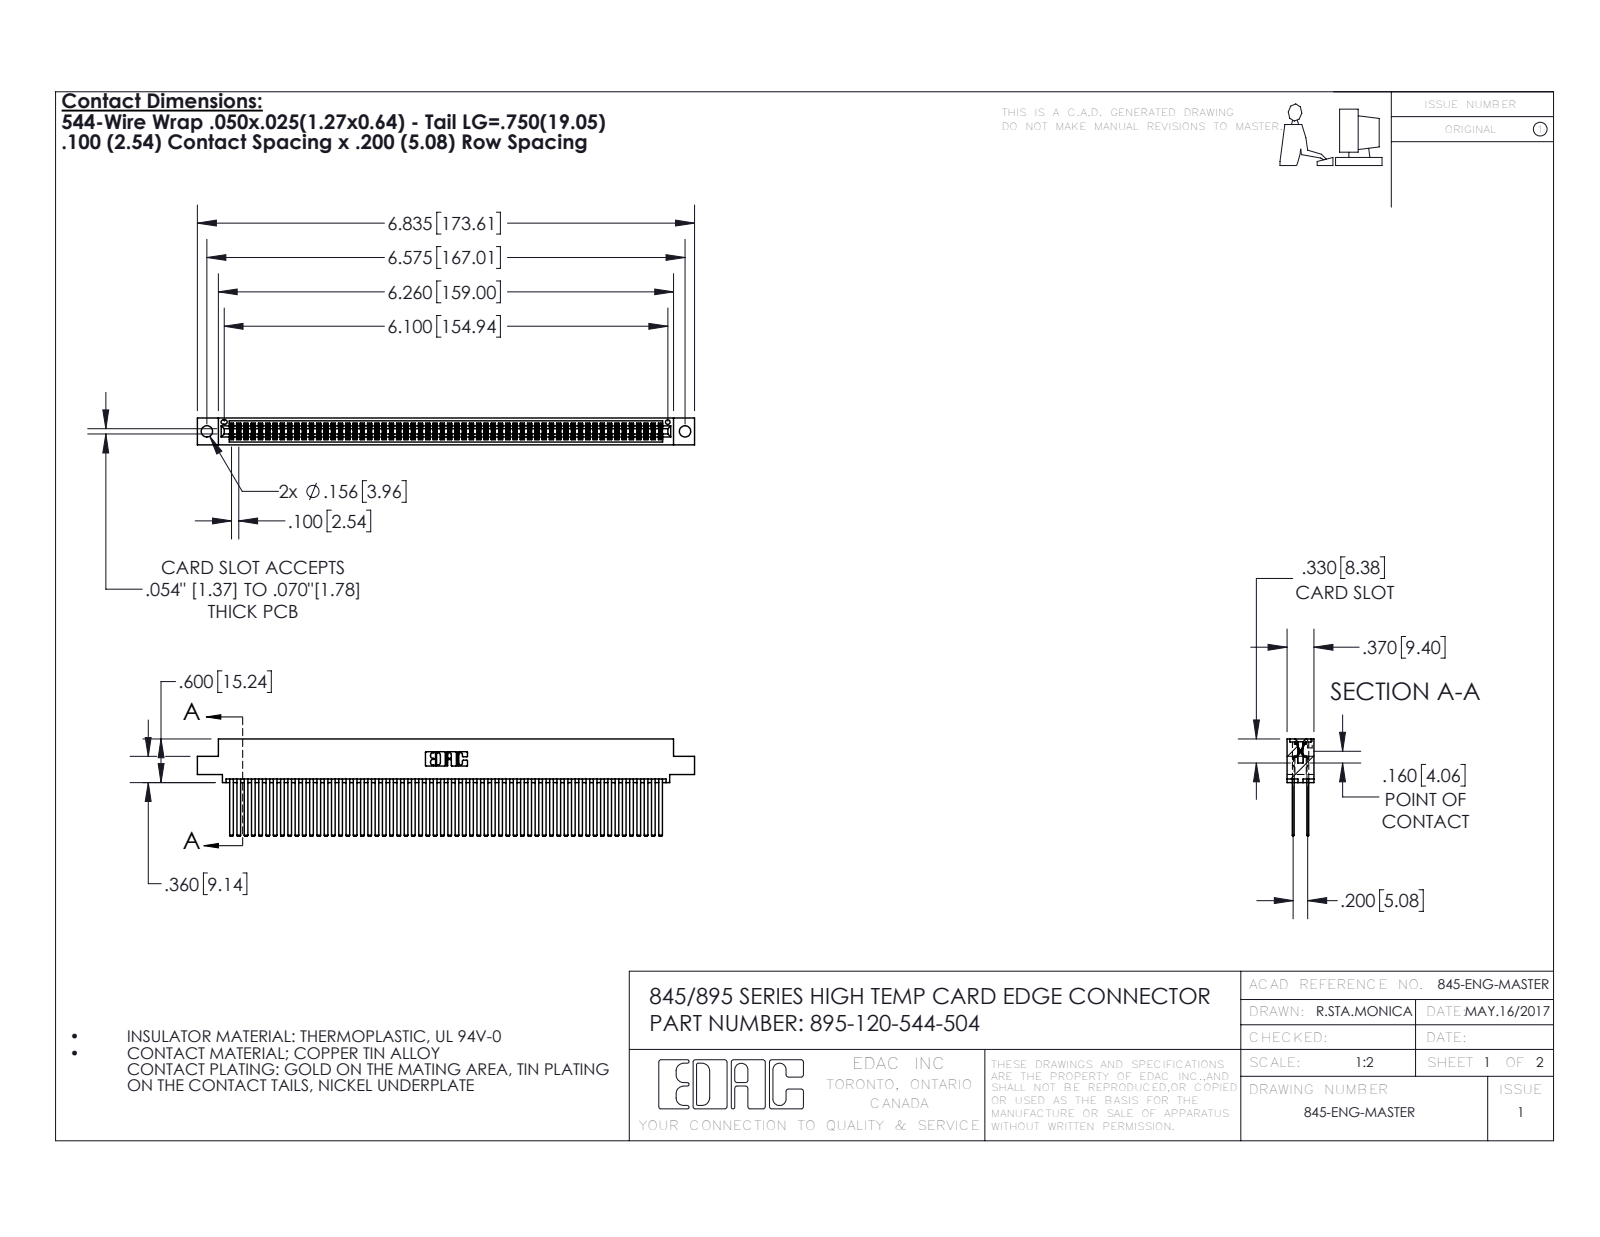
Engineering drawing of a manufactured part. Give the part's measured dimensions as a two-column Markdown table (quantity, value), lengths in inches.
| quantity | value |
| --- | --- |
| part name | 395-120-544-504; 345-292-001_345-293-144; 345 Part_0.110 Offset - 0.156 Dia-TH |
| STEP written by | SolidWorks 2016 (CONFIG_CONTROL_DESIGN) |
| units | inches |
| bodies | 121 solids, 5410 faces (3564 planar, 1846 cylindrical, 0 other) |
| overall size | 6.835 × 1.337 × 0.37 |
| volume | 1.132 in³ |
| surface area | 50.55 in² |
| round holes (diameter × count) | 0.156 × 2, 0.064 × 1 |
| partial cylindrical surfaces (radius × count) | 0.006 × 180, 0.01 × 22, 0.007 × 6, 0.031 × 6, 0.026 × 3, 0.014 × 2, 0.019 × 2, 0.022 × 2 |
| main face-to-face distances | 0.2, 0.025, 0.298, 0.072, 0.098, 0.272, 0.225, 0.175, 0.37, 0.149 |
| hole center spacings | 0.27, 6.339, 6.575 |
